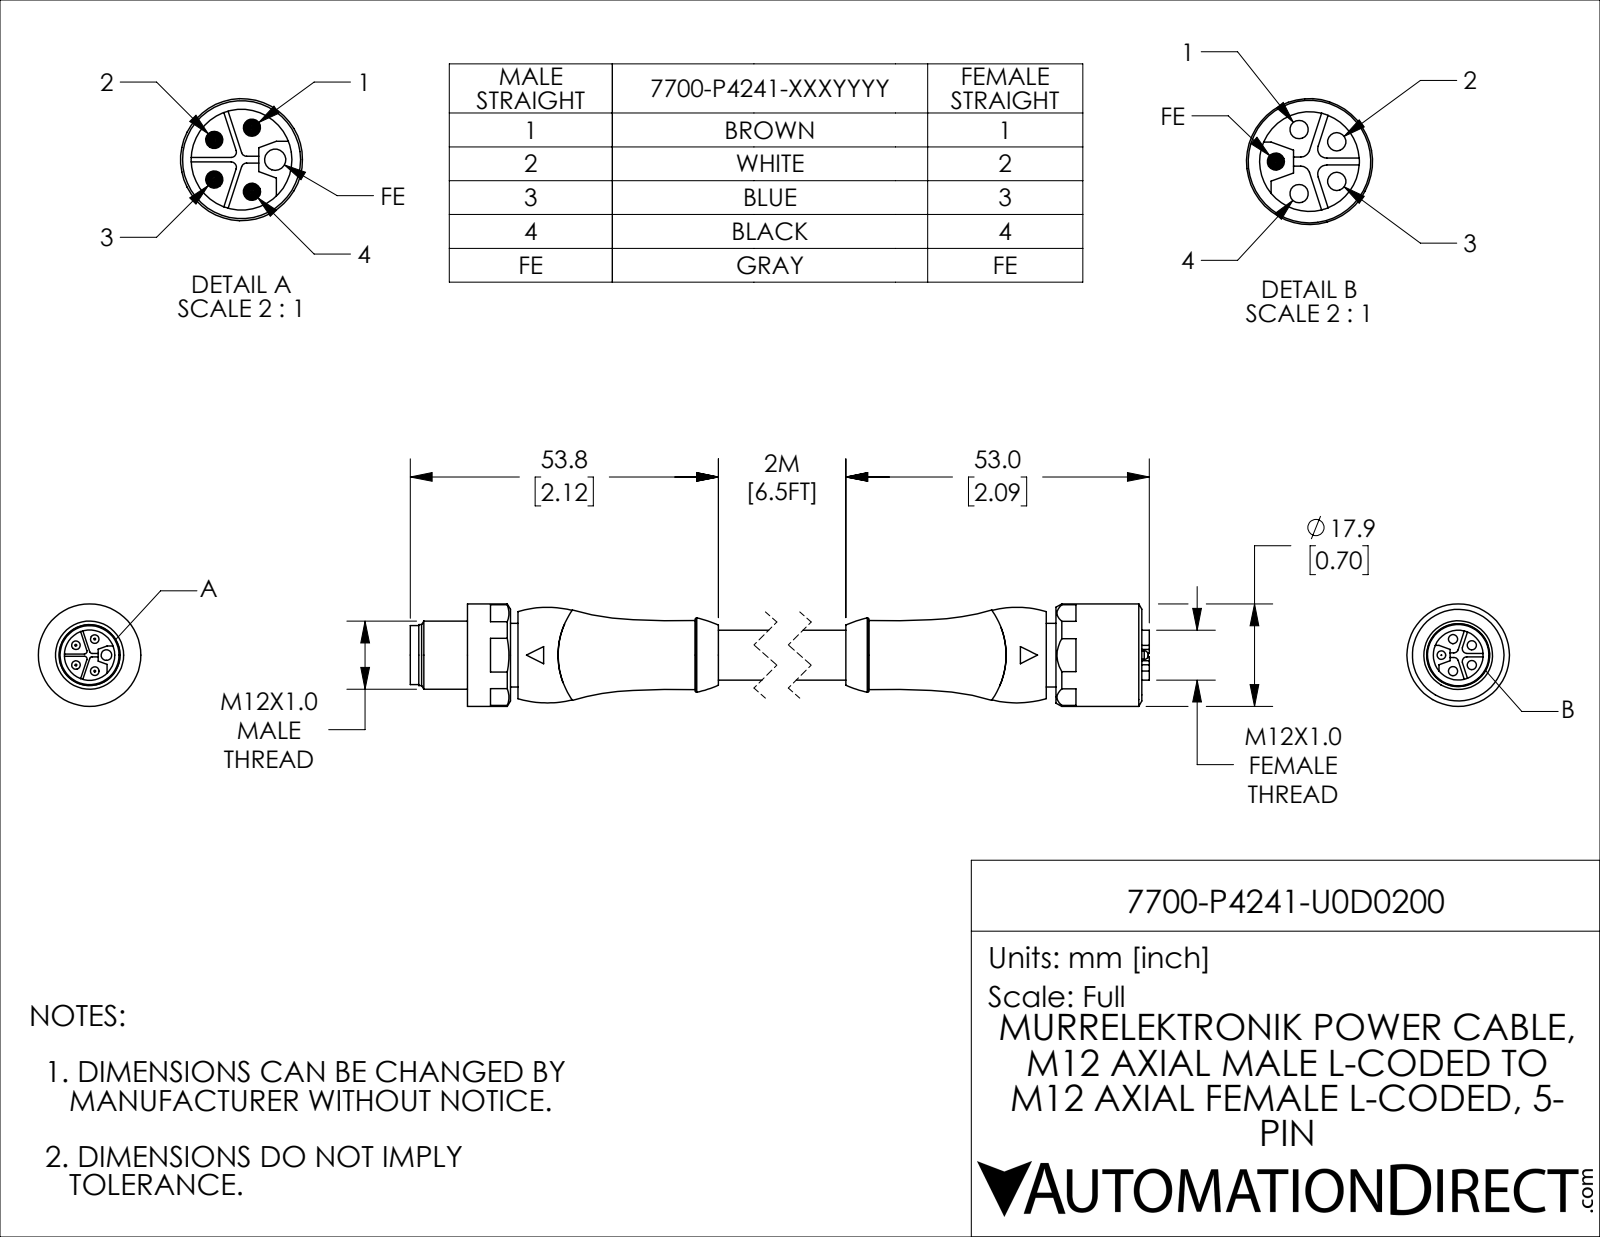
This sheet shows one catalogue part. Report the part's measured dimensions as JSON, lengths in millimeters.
{"part_name": "7700-P4241-U0D0200; 7700-P4241-U0D0200_1; 7700-P4241-U0D0200_2", "step_written_by": "SolidWorks 2021 (CONFIG_CONTROL_DESIGN)", "units": "millimeters", "bodies": {"solids": 3, "faces": 214, "planar": 98, "cylindrical": 62, "other": 54}, "overall_size": [136.8, 17.9, 17.9], "volume_mm3": 17860, "surface_area_mm2": 9316, "round_holes": [[1.6, 4], [1.9, 1], [8.8, 1], [11, 1], [13, 1]], "round_bosses_or_shafts": [[1.5, 5], [17.9, 1], [13, 1], [11.9, 1], [11.1, 1], [10.6, 1], [10.3, 1], [8.7, 1]], "partial_cylinders_radius": [[0.5, 4], [0.8, 4]], "face_to_face_distances": [108.8, 1.7, 8.8, 16.9, 1.3, 7.5, 5.8, 125.5, 16.7, 110.5], "hole_center_spacings": [2.9, 3.5, 5.6, 5.6]}
